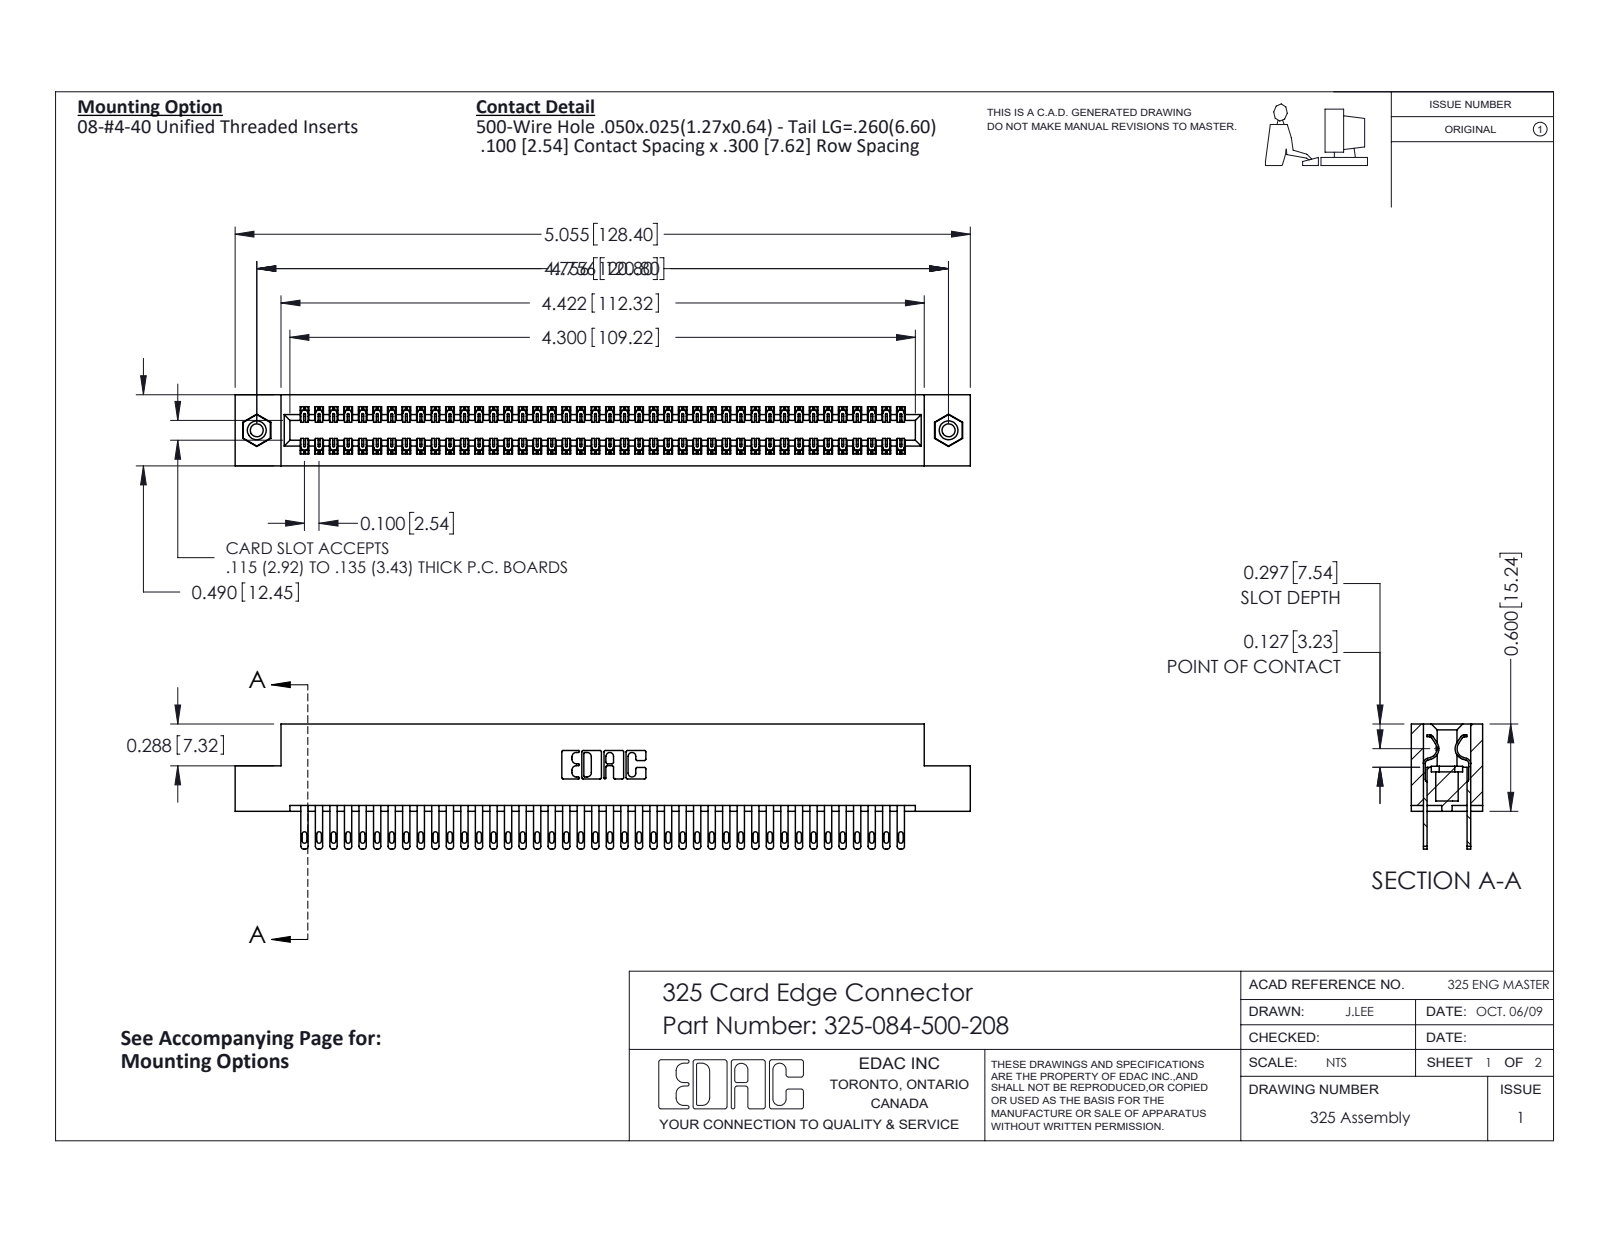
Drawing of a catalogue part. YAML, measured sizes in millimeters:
part_name: "325 Part_TI; 325-084-500-208; 345-250-001_345-250-003-102; 325-292-001_325-293-100"
step_written_by: "SolidWorks 2016 (CONFIG_CONTROL_DESIGN)"
units: millimeters
bodies: {solids: 87, faces: 4206, planar: 2622, cylindrical: 1568, other: 16}
overall_size: [128.4, 21.8, 12.4]
volume: 16830
surface_area: 21260
round_holes:
  - {diameter: 2.3, count: 2}
  - {diameter: 3.2, count: 2}
  - {diameter: 4.1, count: 2}
round_bosses_or_shafts:
  - {diameter: 3.9, count: 2}
partial_cylinders:
  - {radius: 0.2, count: 126}
  - {radius: 0.4, count: 84}
  - {radius: 0.5, count: 84}
  - {radius: 0.3, count: 22}
  - {radius: 0.2, count: 6}
  - {radius: 0.8, count: 6}
  - {radius: 0.7, count: 3}
  - {radius: 0.4, count: 2}
face_to_face_distances: [2.1, 10.3, 7.6, 2.7, 9.7, 0.6, 12.4, 8.3, 7, 14.2]
hole_center_spacings: [120.8]
